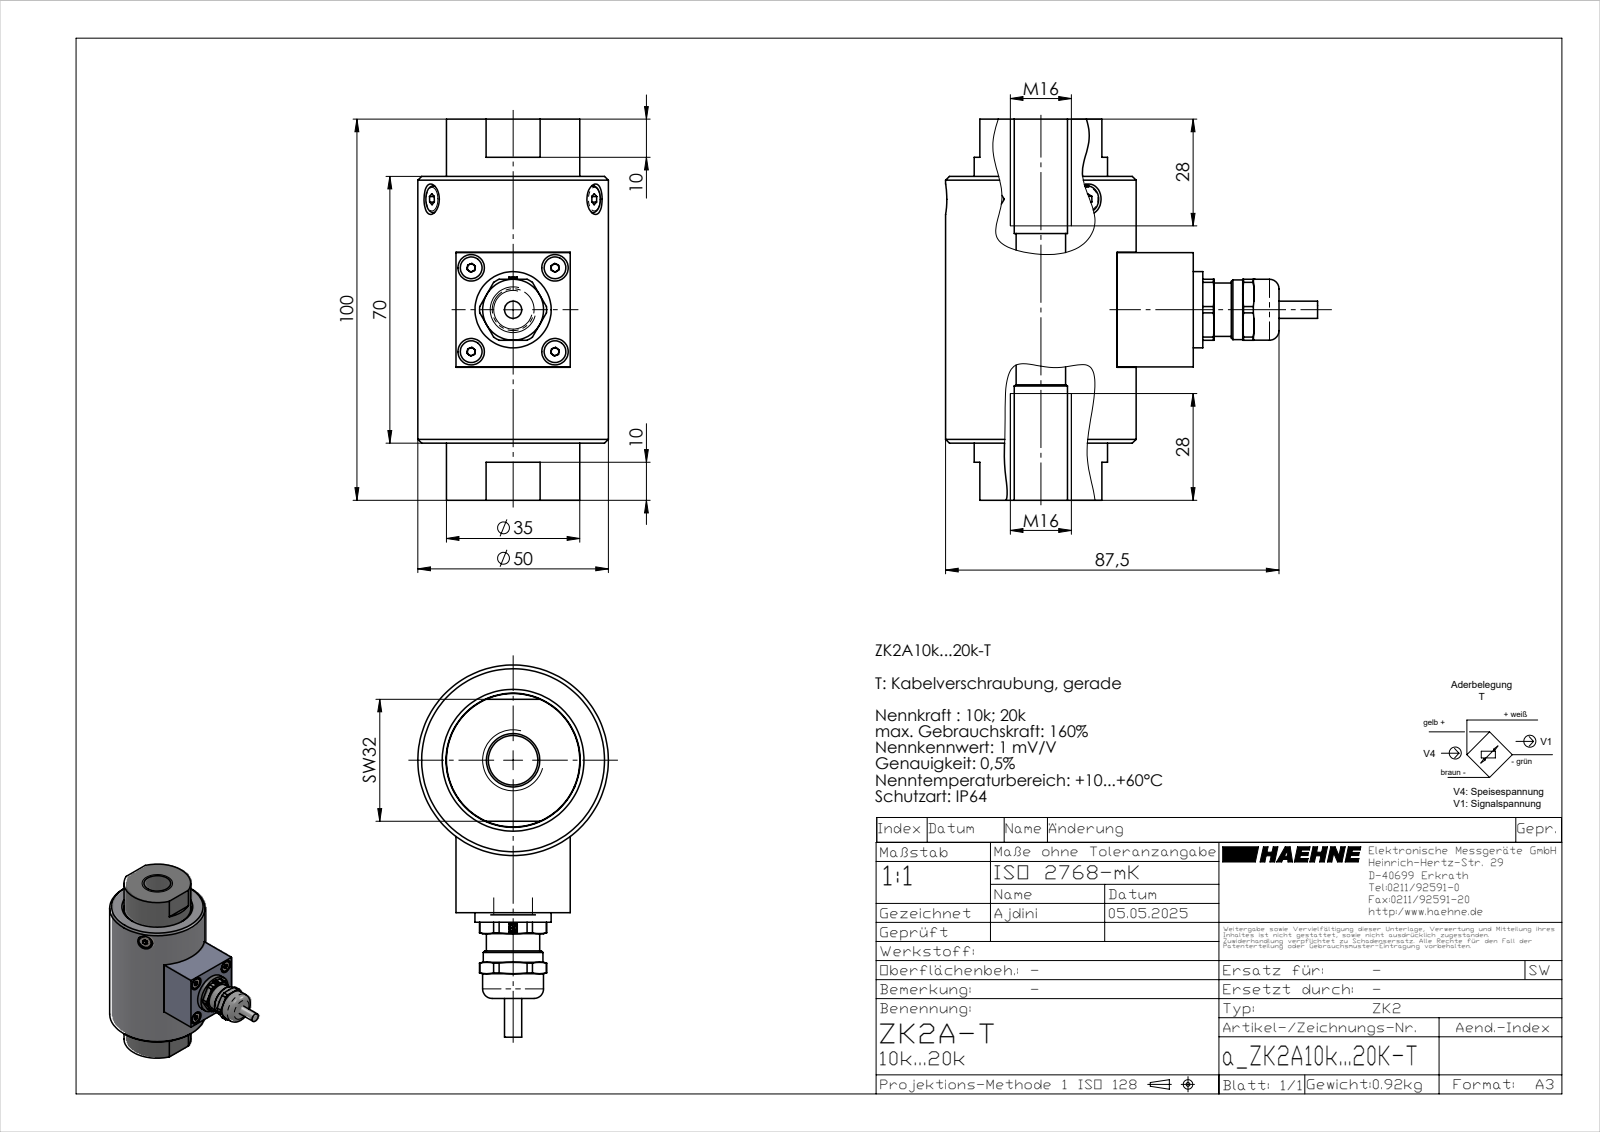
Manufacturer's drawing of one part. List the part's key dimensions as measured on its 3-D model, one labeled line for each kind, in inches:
Part name (STEP PRODUCT): a_ZK2A10k...20K-T
STEP written by: SolidWorks 2023 (AUTOMOTIVE_DESIGN)
Units: inches
Bodies: 13 solids, 329 faces (182 planar, 83 cylindrical, 64 other)
Overall size (bounding box): 3.937 × 3.844 × 1.969
Volume: 9.841 in³ · Surface area: 76.09 in²
Round holes (diameter × count): ⌀0.026 ×10, ⌀0.098 ×4, ⌀0.134 ×4, ⌀0.13 ×3, ⌀0.169 ×3, ⌀0.315 ×3, ⌀0.138 ×1, ⌀0.4 ×1, ⌀0.512 ×1, ⌀0.551 ×1, ⌀0.571 ×1, ⌀0.945 ×1
Round bosses / shafts (diameter × count): ⌀0.224 ×4, ⌀0.118 ×4, ⌀0.276 ×3, ⌀0.157 ×3, ⌀0.079 ×2, ⌀1.969 ×1, ⌀1.378 ×1, ⌀0.787 ×1
Partial cylindrical surfaces — rounded edges, fillets, slot ends (radius × count): R0.346 ×1
Main face-to-face distances: 0.787, 0.591, 3.346, 1.969, 1.181, 1.378, 2.559, 3.937, 2.756, 0.886
Hole centre spacings: 0.045, 0.028, 0.028, 0.474, 0.613, 0.866, 0.276, 0.304
